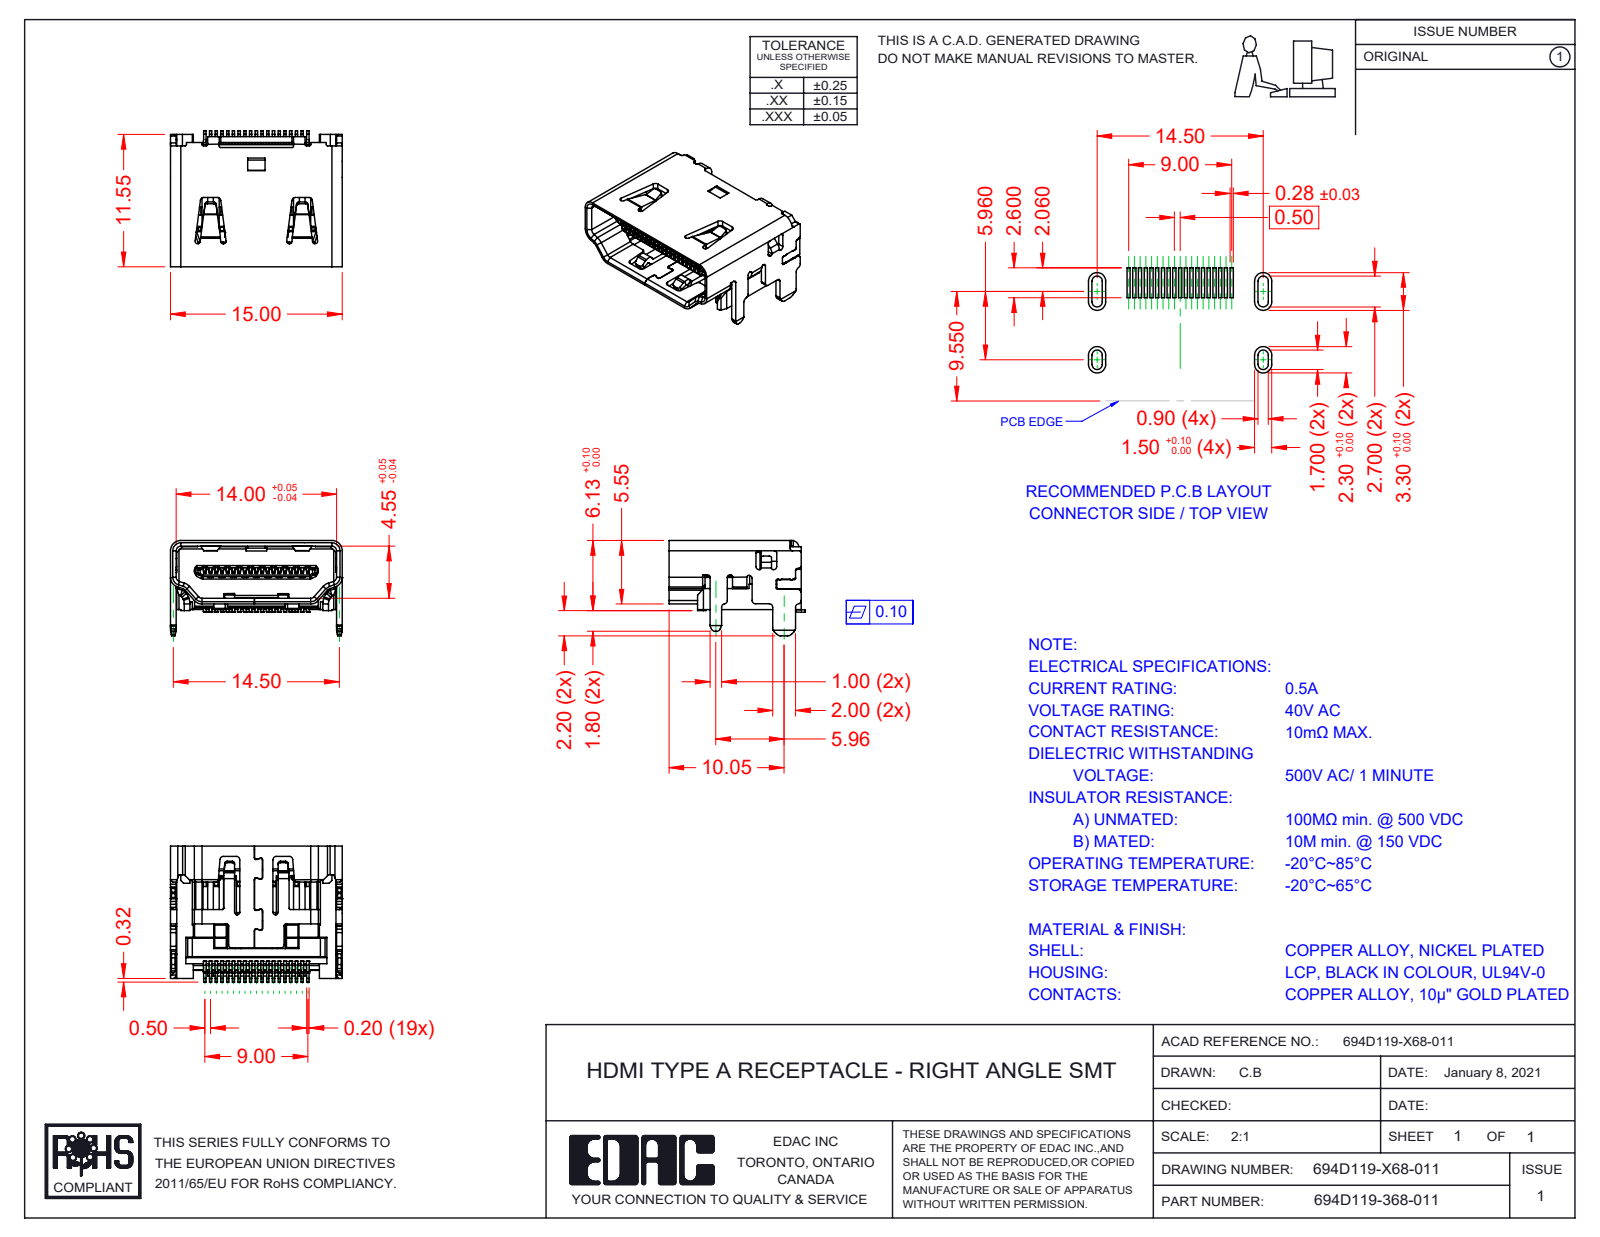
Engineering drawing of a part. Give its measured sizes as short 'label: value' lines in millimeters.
name: Insulator 694D119-X68-011; Contacts 694D119-X68-011; 694D119-168-011; Shell 694D119-X68-011
written by: SolidWorks 2020 (AUTOMOTIVE_DESIGN)
unit: mm
bodies: 21 solids, 3408 faces (2227 planar, 1102 cylindrical, 79 other)
size: 15 × 11.87 × 8.33
volume: 463 mm³; area: 1 882 mm²
rounds: 111× R0.2, 93× R0.15, 50× R0.1, 35× R0.13, 27× R0.3, 20× R0.11, 11× R0.5, 8× R0.35
face distances: 0.5, 0.7, 2.53, 0.55, 4.55, 3.03, 14.5, 0.35, 0.9, 2.33
